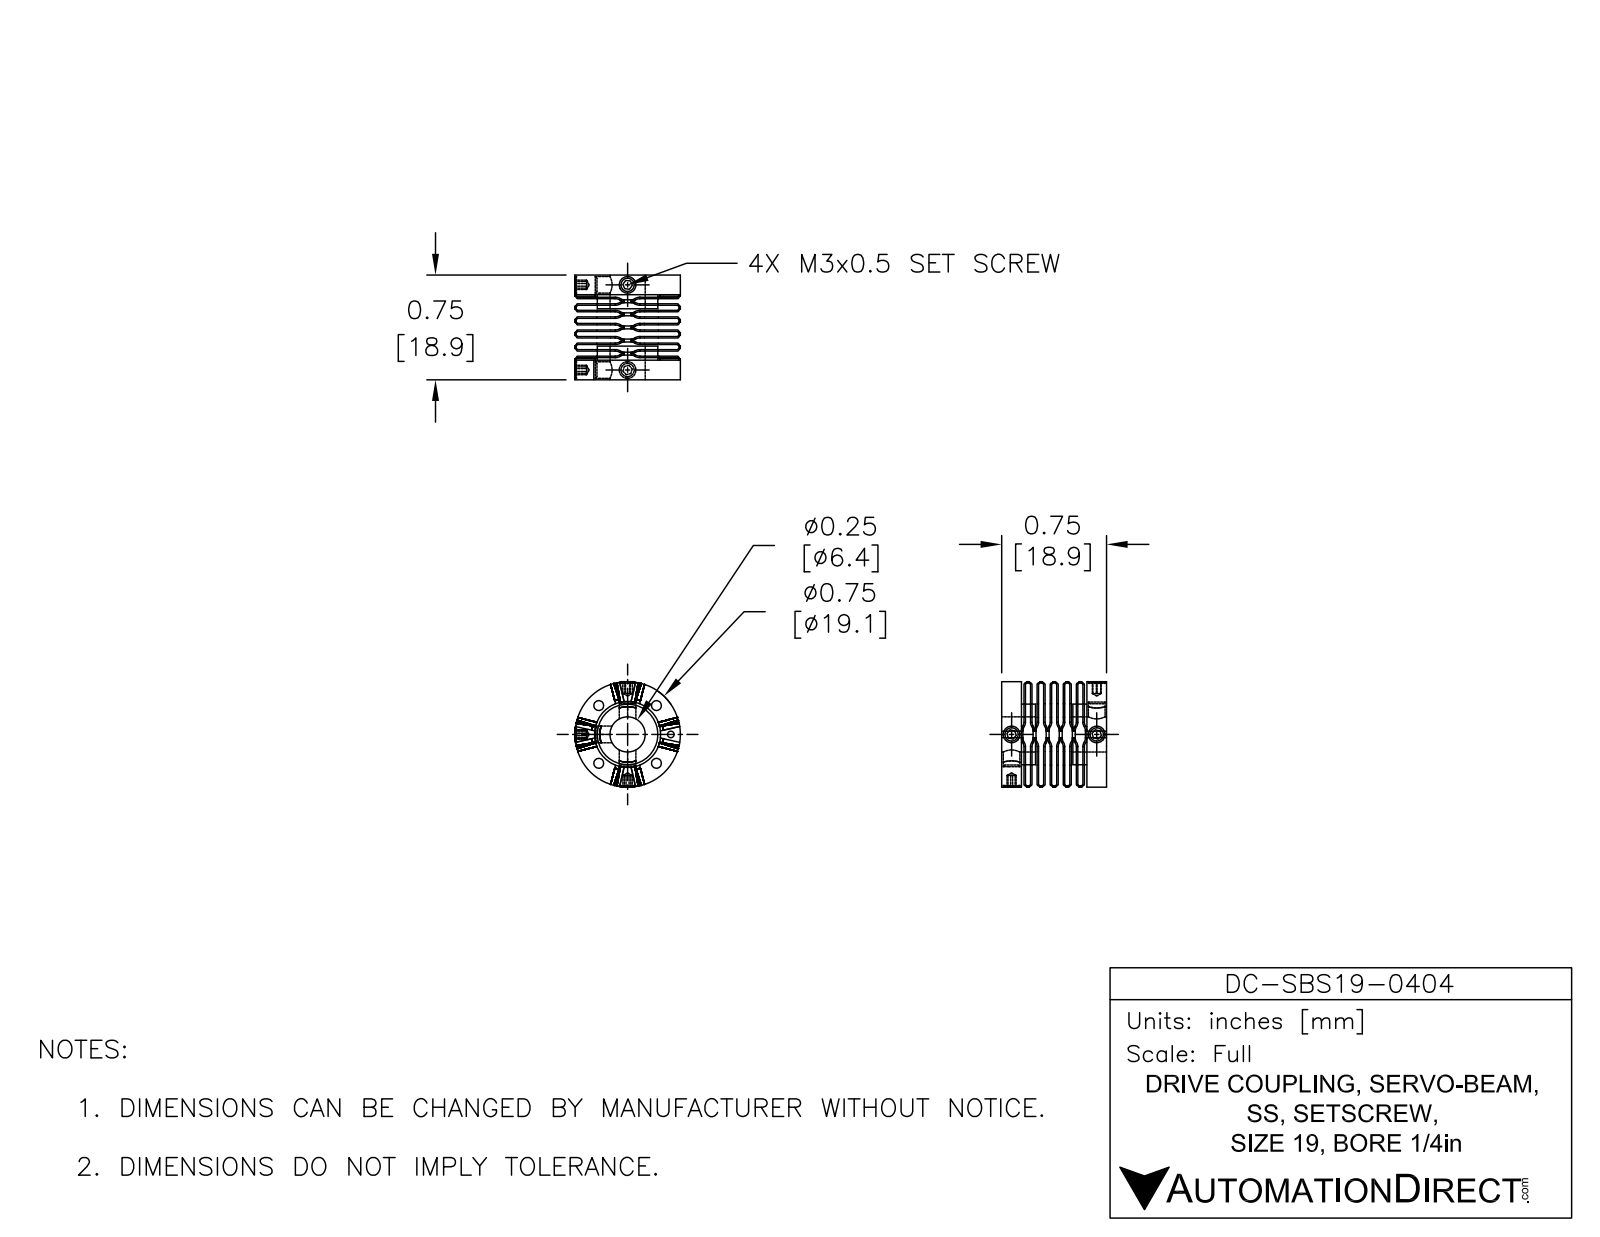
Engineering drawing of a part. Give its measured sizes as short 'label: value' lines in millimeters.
name: DC-SBS19-0404
written by: SolidWorks 2015 (AUTOMOTIVE_DESIGN)
unit: mm
bodies: 16 solids, 878 faces (362 planar, 508 cylindrical, 8 other)
size: 19.5 × 19.27 × 18.92
volume: 2 410 mm³; area: 5 971 mm²
holes: 4× ⌀1.78, 4× ⌀2.2, 1× ⌀1.19, 1× ⌀6.35, 1× ⌀11.91
bosses: 3× ⌀2.5, 1× ⌀19.05, 1× ⌀10.92, 1× ⌀2.39
rounds: 320× R0.7
face distances: 2.36, 4.72, 7.08, 1.17, 0.9, 2.63, 3.53, 3.56, 15.36, 3.26
hole spacings: 7.37, 10.42, 5.82, 14.02, 14.74, 7.81, 15.82
